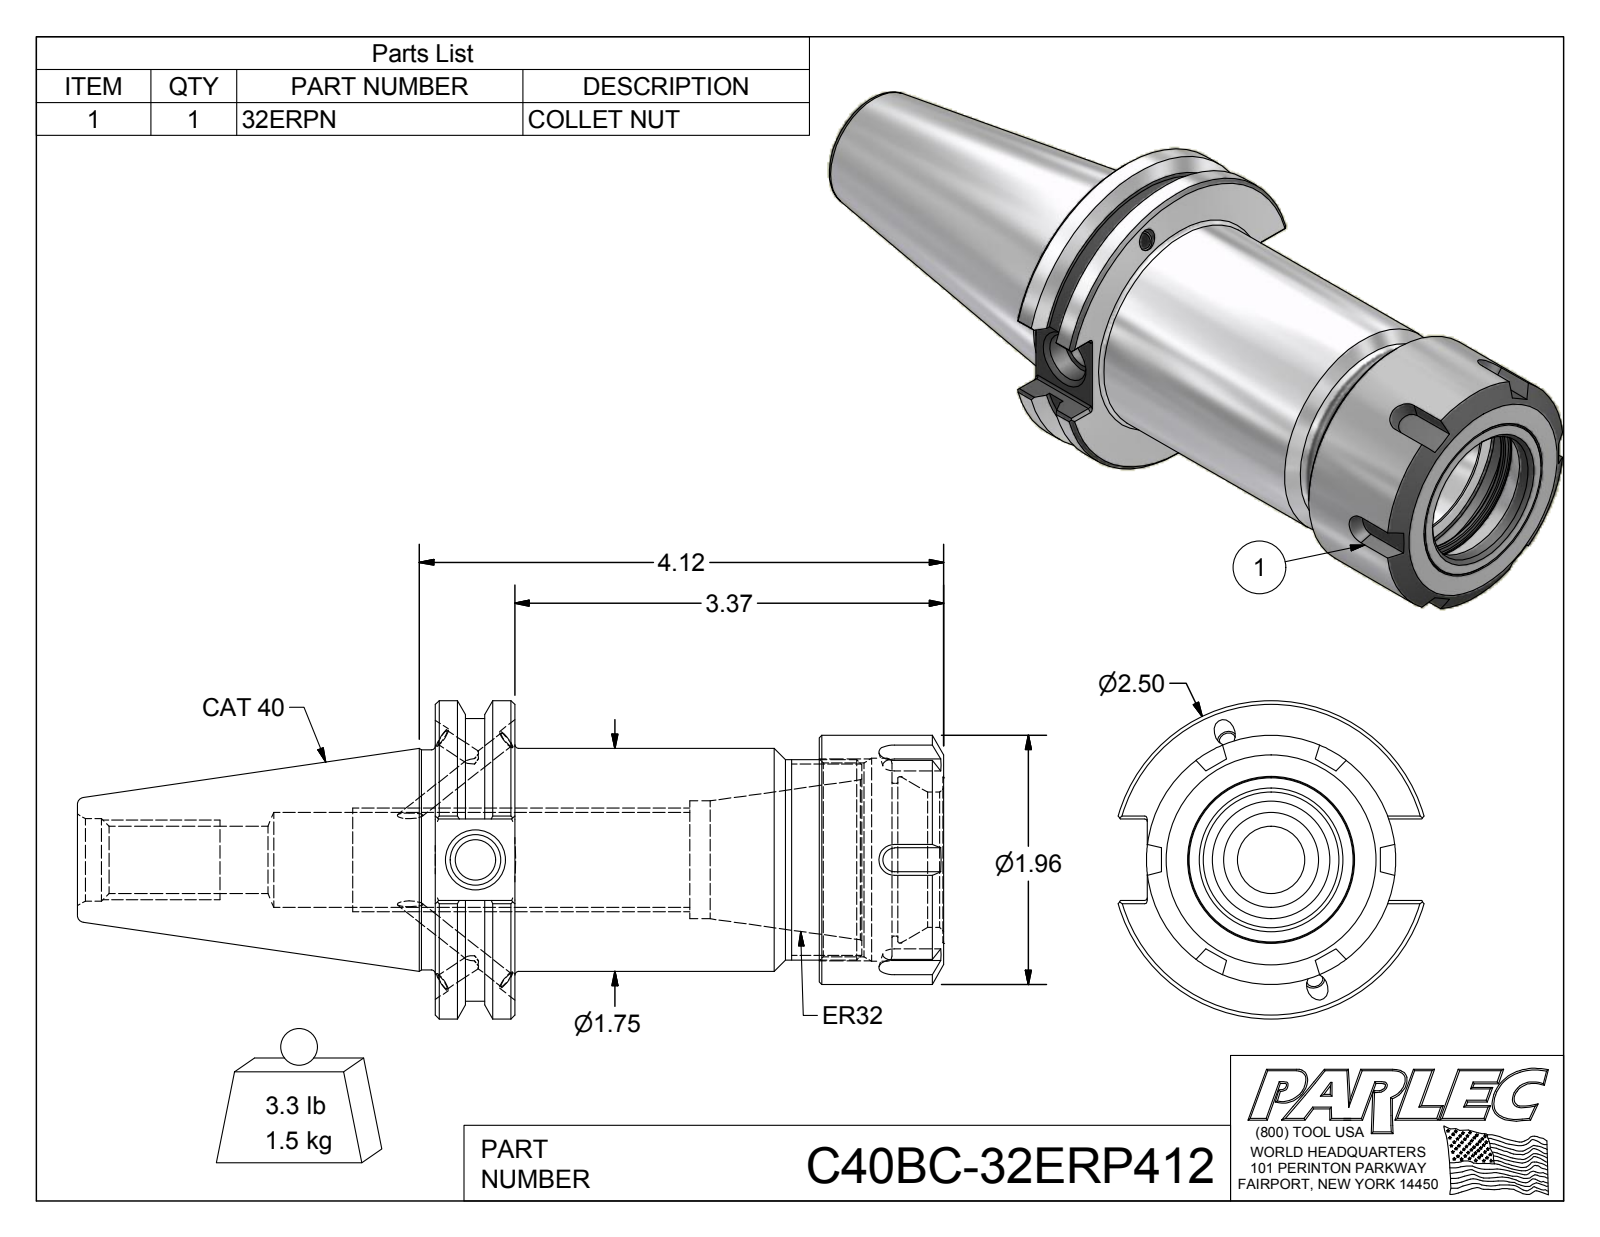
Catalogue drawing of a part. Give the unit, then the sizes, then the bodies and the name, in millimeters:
Units: millimetres
Overall size (bounding box): 172.91 × 63.5 × 61.05
Round holes (diameter × count): ⌀3.3 ×4, ⌀4.1 ×4, ⌀8 ×1, ⌀10.13 ×1, ⌀13.39 ×1, ⌀16.46 ×1, ⌀18.92 ×1, ⌀23.5 ×1, ⌀27 ×1, ⌀30.48 ×1, ⌀33.15 ×1, ⌀38.68 ×1
Round bosses / shafts (diameter × count): ⌀4.2 ×4, ⌀4 ×4, ⌀63.5 ×1, ⌀56.36 ×1, ⌀49.73 ×1, ⌀44.45 ×1, ⌀43.94 ×1, ⌀40 ×1
Partial cylindrical surfaces — rounded edges, fillets, slot ends (radius × count): R0.51 ×12
Main face-to-face distances: 15.87, 101.47, 85.6, 76.63, 60.76, 24.84, 6.04, 85.09, 91.13, 75.26
Volume: 187 516 mm³ · Surface area: 45 275 mm²
Bodies: 6 solids, 209 faces (99 planar, 53 cylindrical, 57 other)
Part name (STEP PRODUCT): 32ERPN; C40BC-32ER4-1; 029-965; C40BC-32ERP412
STEP written by: Autodesk Inventor 2016 (AUTOMOTIVE_DESIGN)
